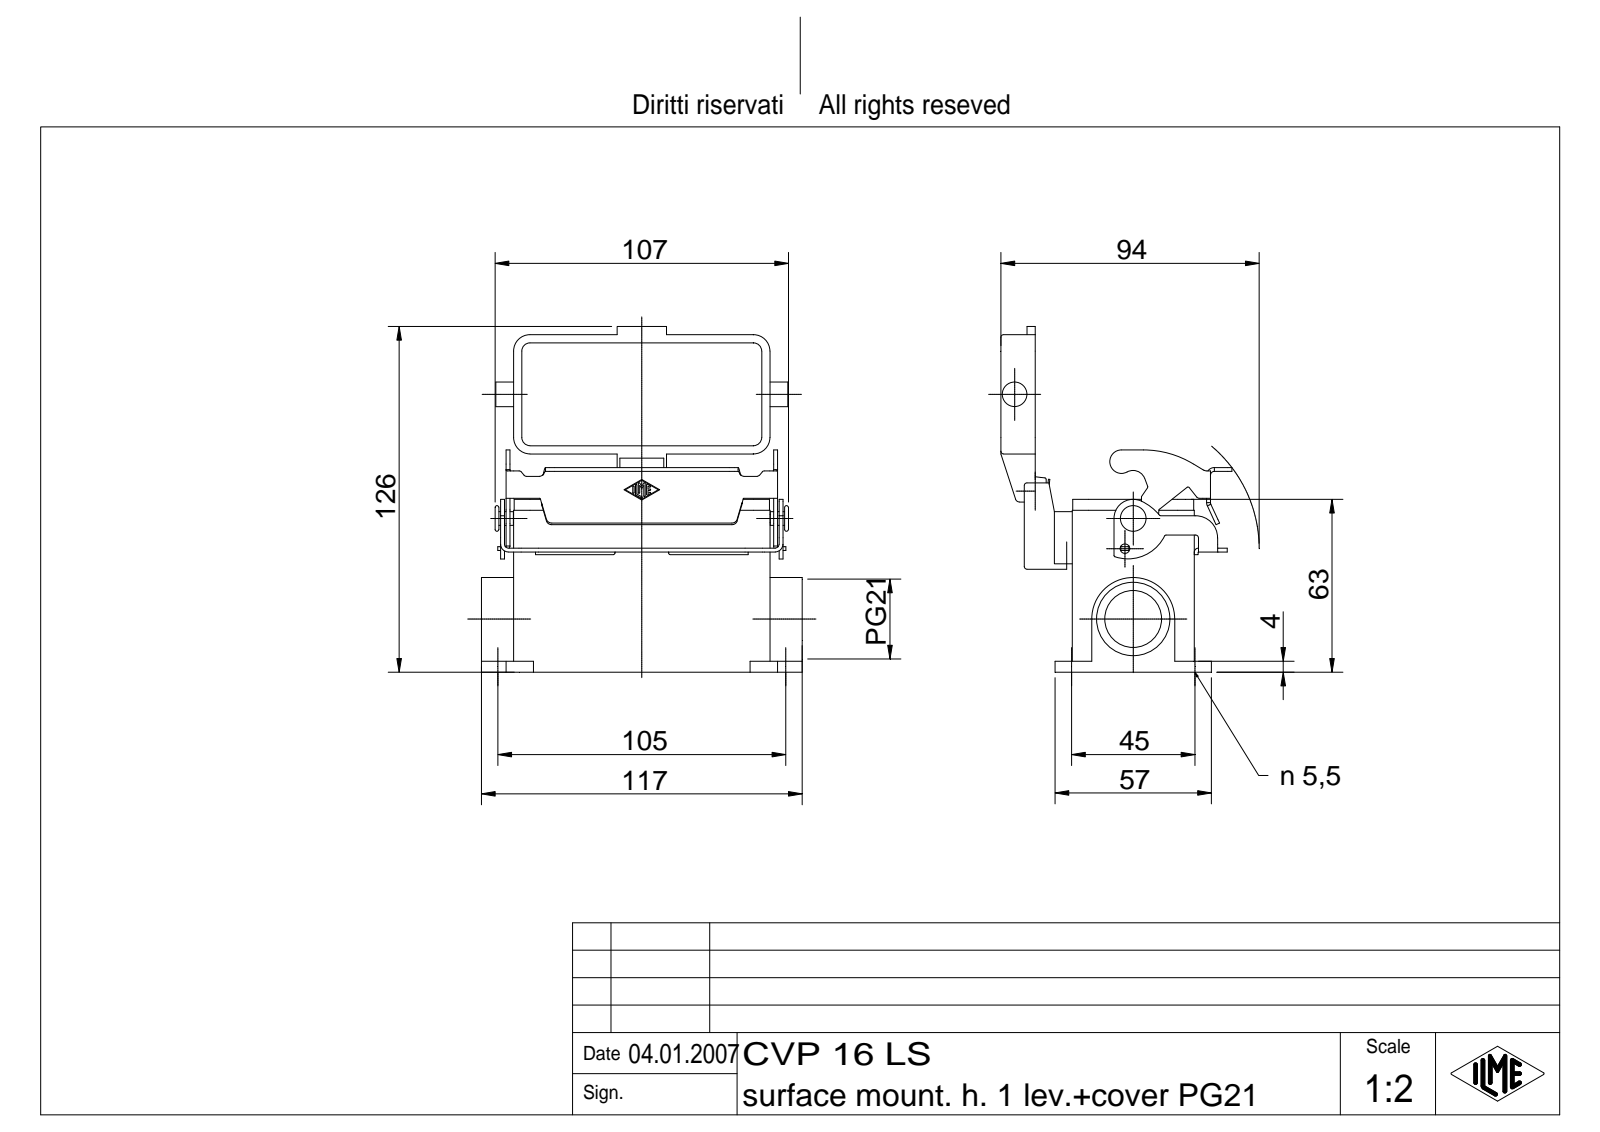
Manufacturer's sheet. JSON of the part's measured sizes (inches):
{"part_name": "CVP 16 LS", "step_written_by": "Autodesk Inventor 7 (AUTOMOTIVE_DESIGN)", "units": "inches", "bodies": {"solids": 4, "faces": 572, "planar": 222, "cylindrical": 185, "other": 165}, "overall_size": [4.961, 4.606, 3.316], "volume_in3": 8.304, "surface_area_in2": 122.4, "round_holes": [[0.217, 4], [0.138, 1], [0.157, 1], [0.818, 1], [1.054, 1]], "round_bosses_or_shafts": [[0.197, 2], [0.354, 1], [0.276, 1], [0.126, 1], [0.118, 1]], "partial_cylinders_radius": [[0.039, 27], [0.01, 15], [0.02, 10], [0.059, 10], [0.236, 8], [0.079, 7], [0.055, 6], [0.11, 6]], "face_to_face_distances": [0.157, 1.594, 1.752, 2.776, 1.437, 2.618, 1.181, 1.024, 0.098, 0.925], "hole_center_spacings": [1.772, 4.134, 4.498, 1.015]}
